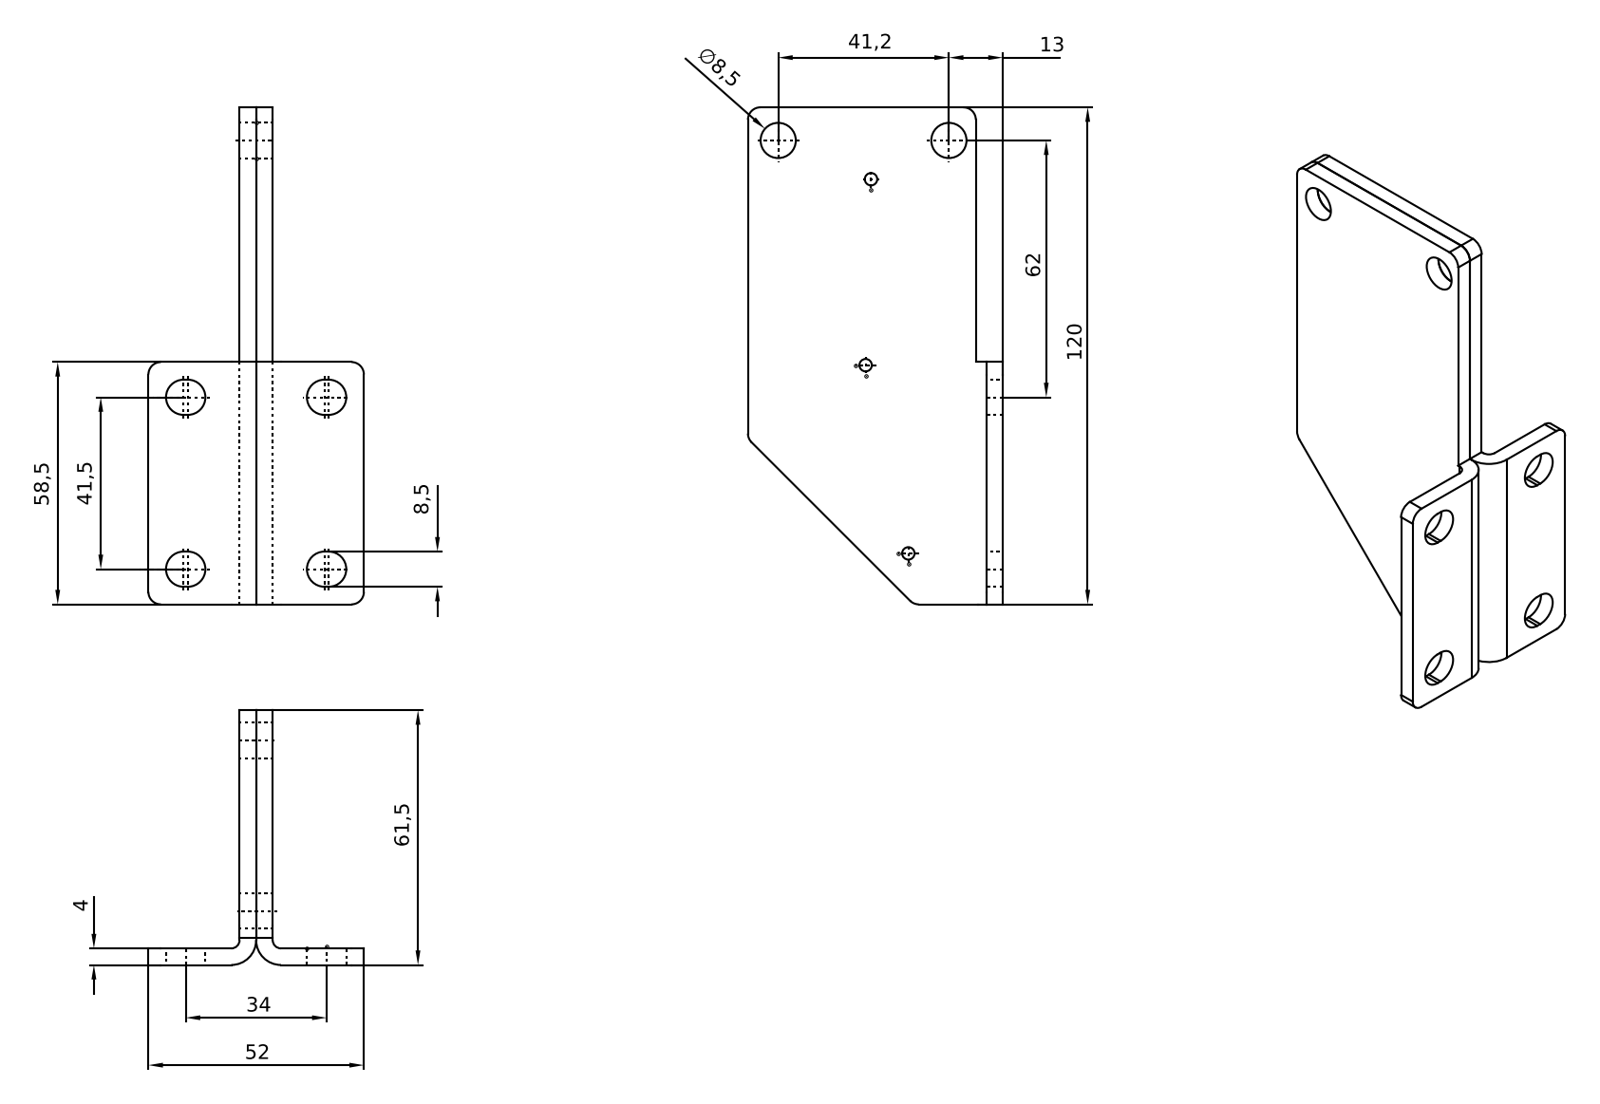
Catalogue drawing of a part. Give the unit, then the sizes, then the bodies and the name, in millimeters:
Units: millimetres
Overall size (bounding box): 120 × 61.5 × 52
Partial cylindrical surfaces — rounded edges, fillets, slot ends (radius × count): R3 ×6, R4.25 ×4, R2 ×1, R6 ×1
Main face-to-face distances: 4, 61.5, 57.5, 6.5, 2.5, 55, 120, 22, 58.5, 4.25
Volume: 56 918 mm³ · Surface area: 20 920 mm²
Bodies: 1 solid, 58 faces (14 planar, 18 cylindrical, 26 other)
STEP written by: Autodesk Inventor 8 (AUTOMOTIVE_DESIGN)
